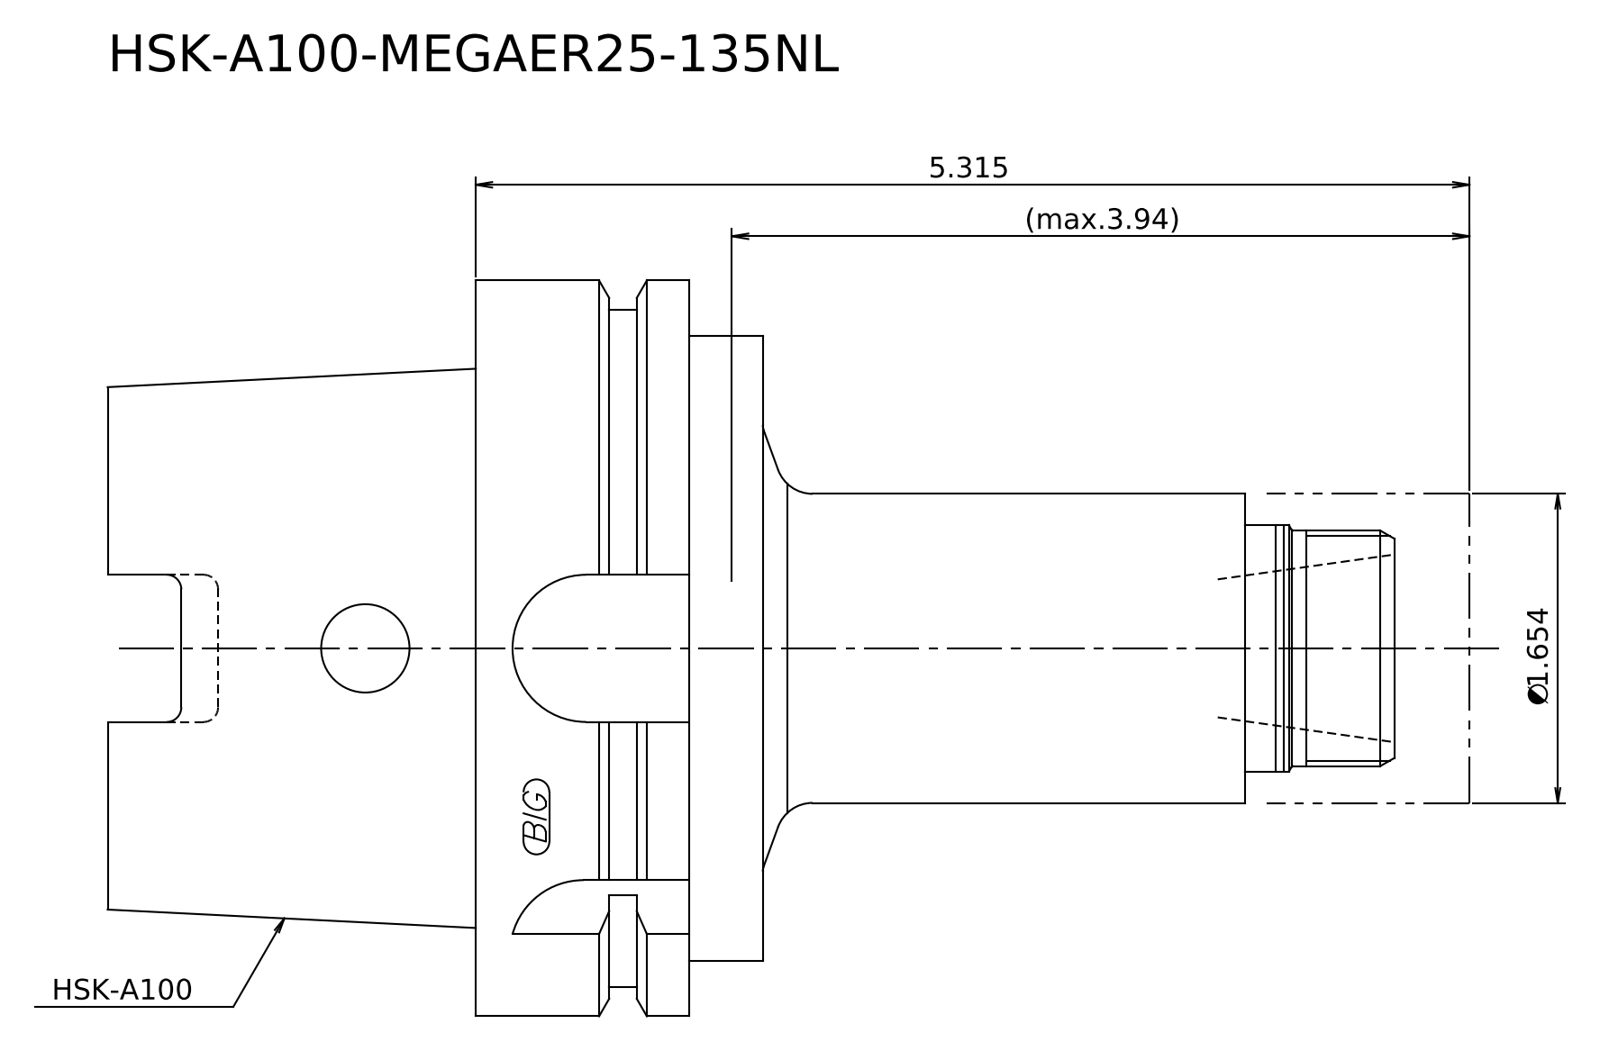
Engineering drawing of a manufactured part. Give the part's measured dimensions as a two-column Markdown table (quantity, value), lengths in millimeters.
| quantity | value |
| --- | --- |
| STEP written by | Kubotek KeyCreator 2011 V10.0.2 (22737) (automotive_design) |
| units | millimeters |
| bodies | 2 solids, 24 faces (10 planar, 8 cylindrical, 6 other) |
| overall size | 185 × 100 × 100 |
| volume | 641 526 mm³ |
| surface area | 56 609 mm² |
| round bosses / shafts (diameter × count) | 100 × 1, 92 × 1, 85 × 1, 42 × 1, 33.5 × 1, 32 × 1 |
| main face-to-face distances | 50, 39, 89, 10, 29, 79, 68.5, 78.5, 107.5, 157.5 |
